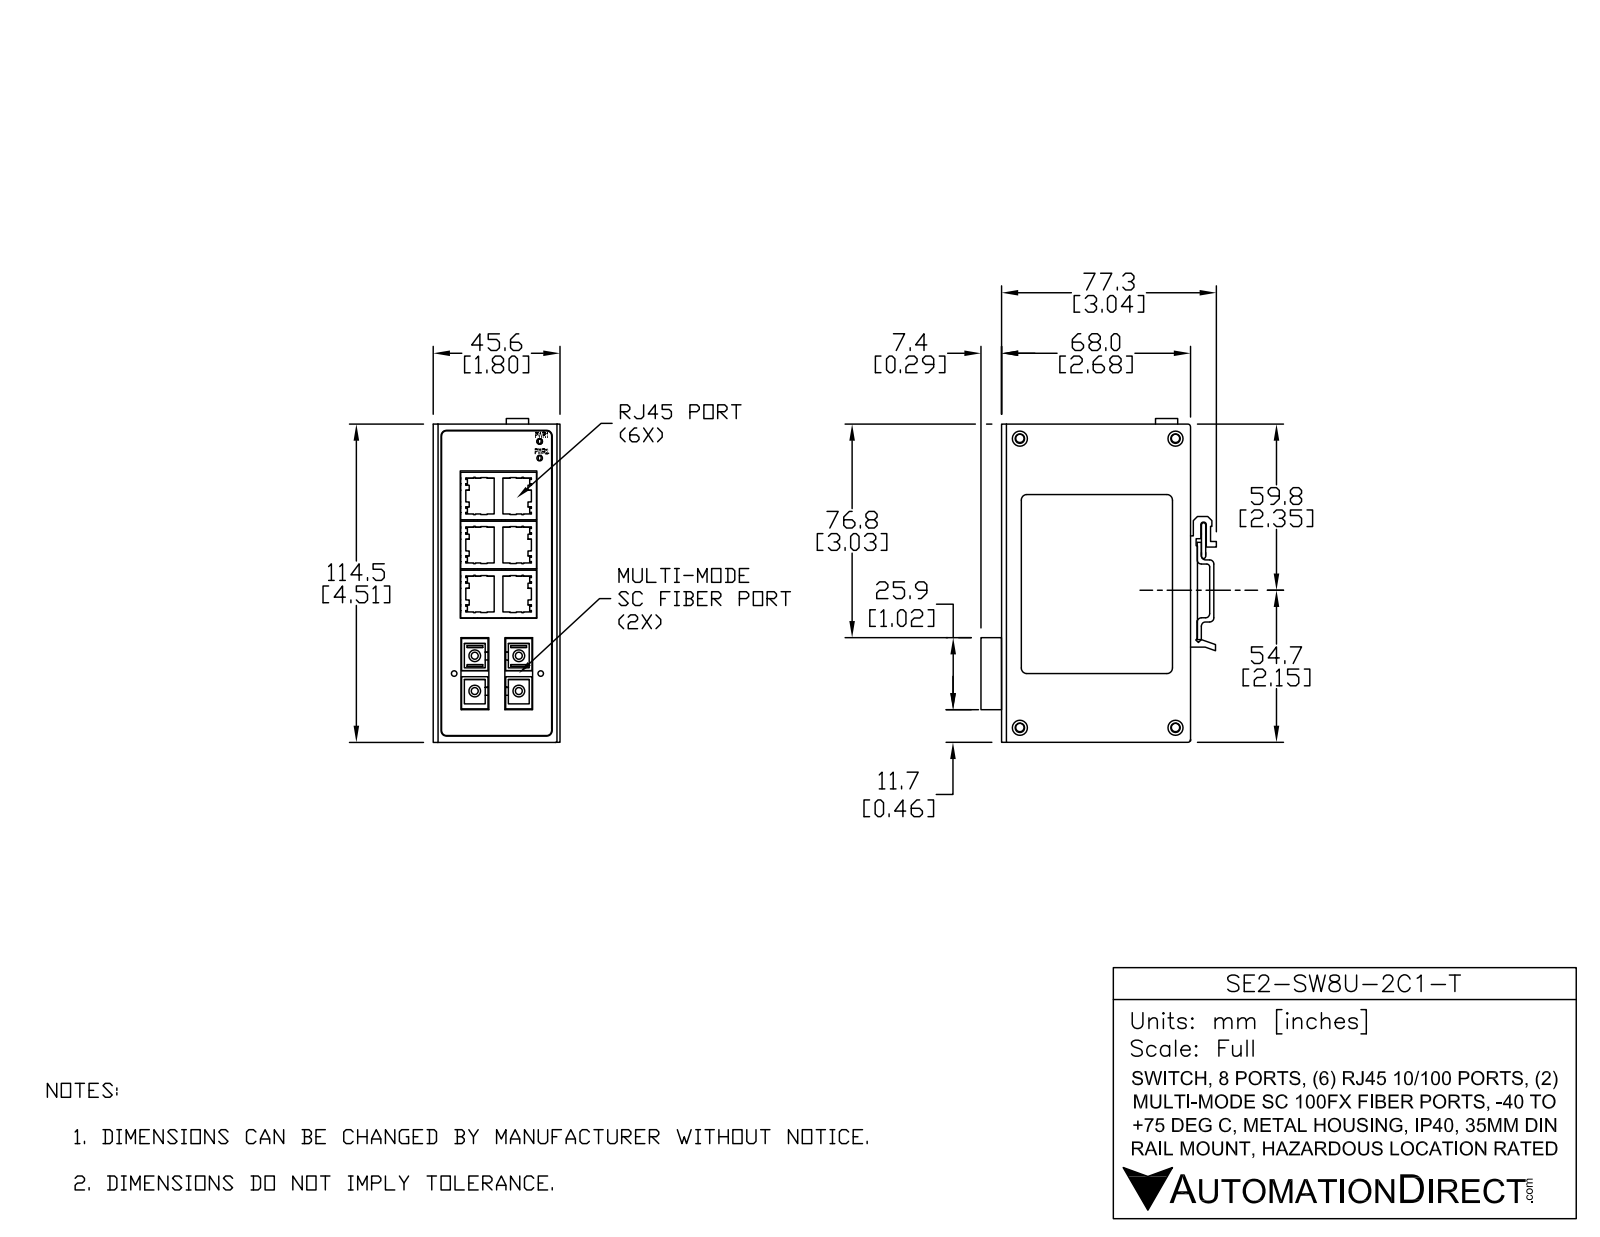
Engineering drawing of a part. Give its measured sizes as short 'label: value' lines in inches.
name: SE2-SW8U-2C1-T
written by: SolidWorks 2017 (AUTOMOTIVE_DESIGN)
unit: in
bodies: 6 solids, 473 faces (426 planar, 17 cylindrical, 30 other)
size: 4.508 × 3.402 × 1.795
volume: 21.66 in³; area: 65.47 in²
holes: 4× ⌀0.099
bosses: 3× ⌀0.165, 1× ⌀0.165
rounds: 9× R0.039
face distances: 1.795, 2.661, 4.508, 0.098, 2.76, 2.776, 2.677, 0.016, 0.039, 2.378
hole spacings: 0.5, 0.625, 0.8
